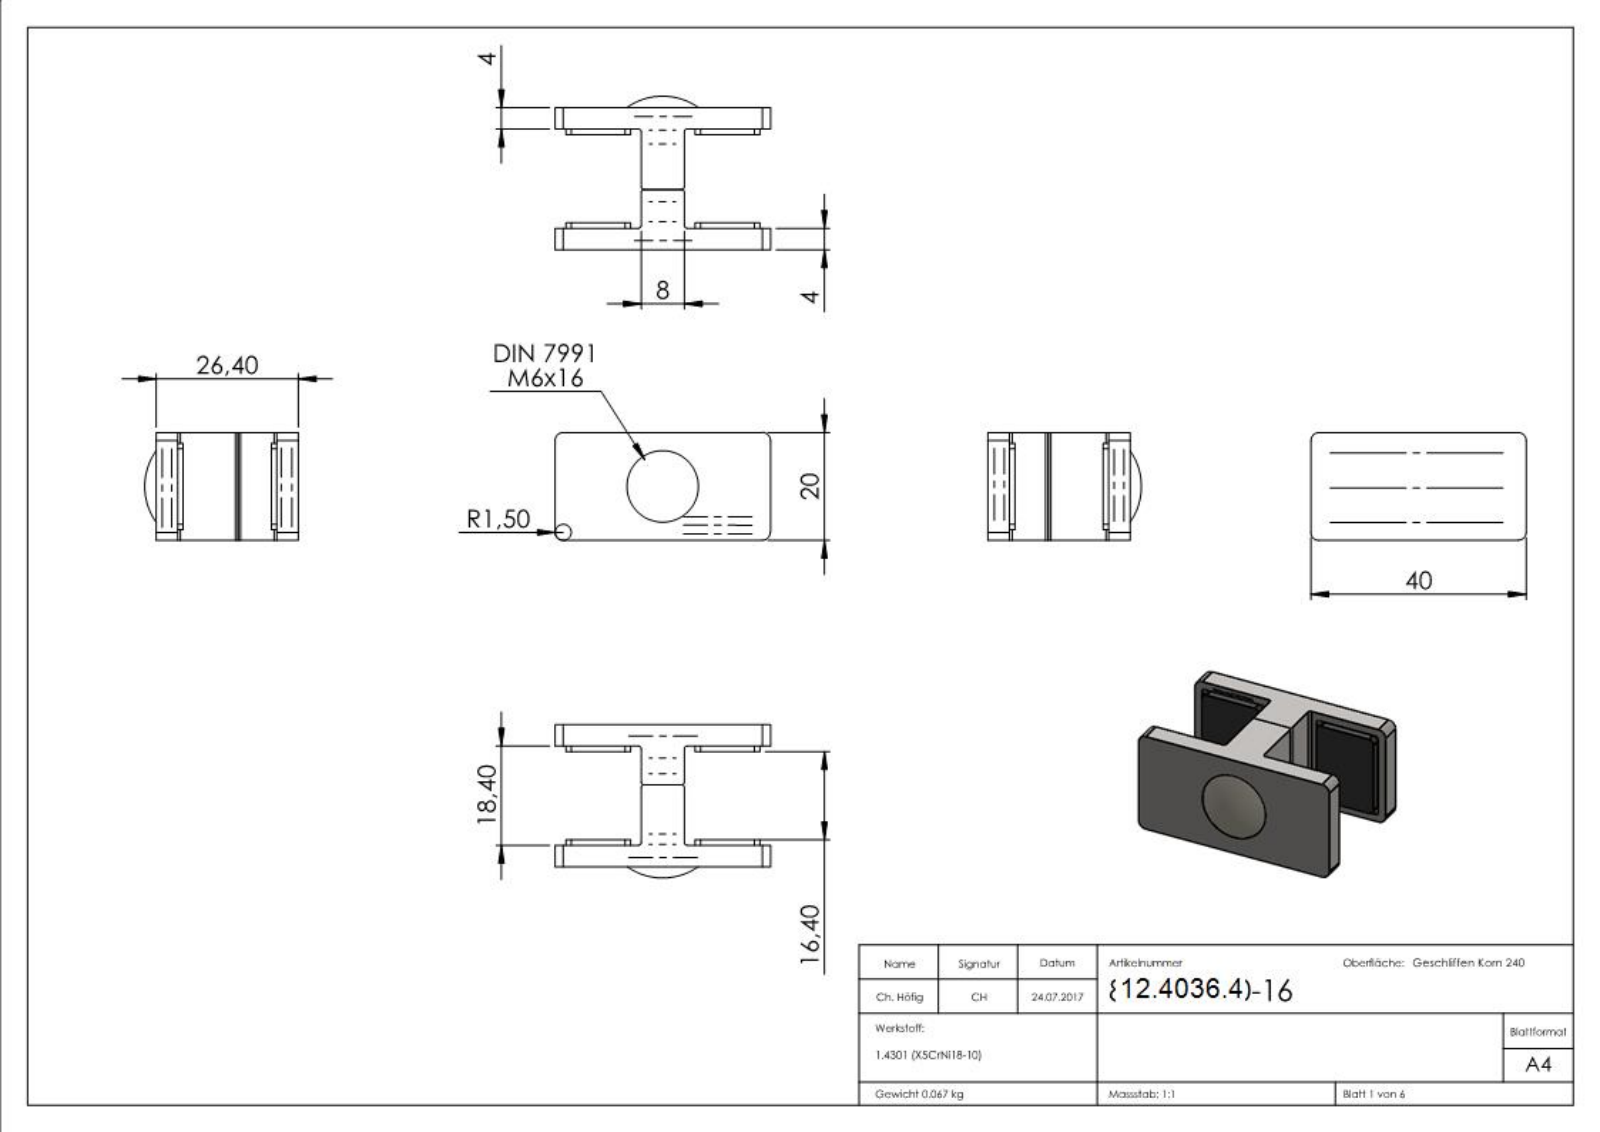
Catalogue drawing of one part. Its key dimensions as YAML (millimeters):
part_name: "80570-XXX-XX Teil4_80570-XXX-XX Teil4; 80570-240-16; DIN7991 M6xXX_DIN7991 M6x22; 80570-XXX-XX Teil2_80570-240-16 Teil2 (+7 more)"
step_written_by: "SolidWorks 2018 (CONFIG_CONTROL_DESIGN)"
units: millimeters
bodies: {solids: 8, faces: 886, planar: 381, cylindrical: 227, other: 278}
overall_size: [40, 28.51, 20]
volume: 9811
surface_area: 8891
round_holes:
  - {diameter: 2.7, count: 2}
  - {diameter: 1.8, count: 1}
  - {diameter: 5, count: 1}
  - {diameter: 6.5, count: 1}
  - {diameter: 12.5, count: 1}
round_bosses_or_shafts:
  - {diameter: 12, count: 1}
  - {diameter: 6, count: 1}
  - {diameter: 4, count: 1}
partial_cylinders:
  - {radius: 0.5, count: 80}
  - {radius: 0.1, count: 18}
  - {radius: 0.2, count: 12}
  - {radius: 1, count: 8}
  - {radius: 0.19, count: 4}
  - {radius: 1.5, count: 4}
face_to_face_distances: [3.5, 22.9, 1.5, 5, 26.4, 21.4, 17.9, 19.4, 2, 0.5]
hole_center_spacings: [6.5, 13]
